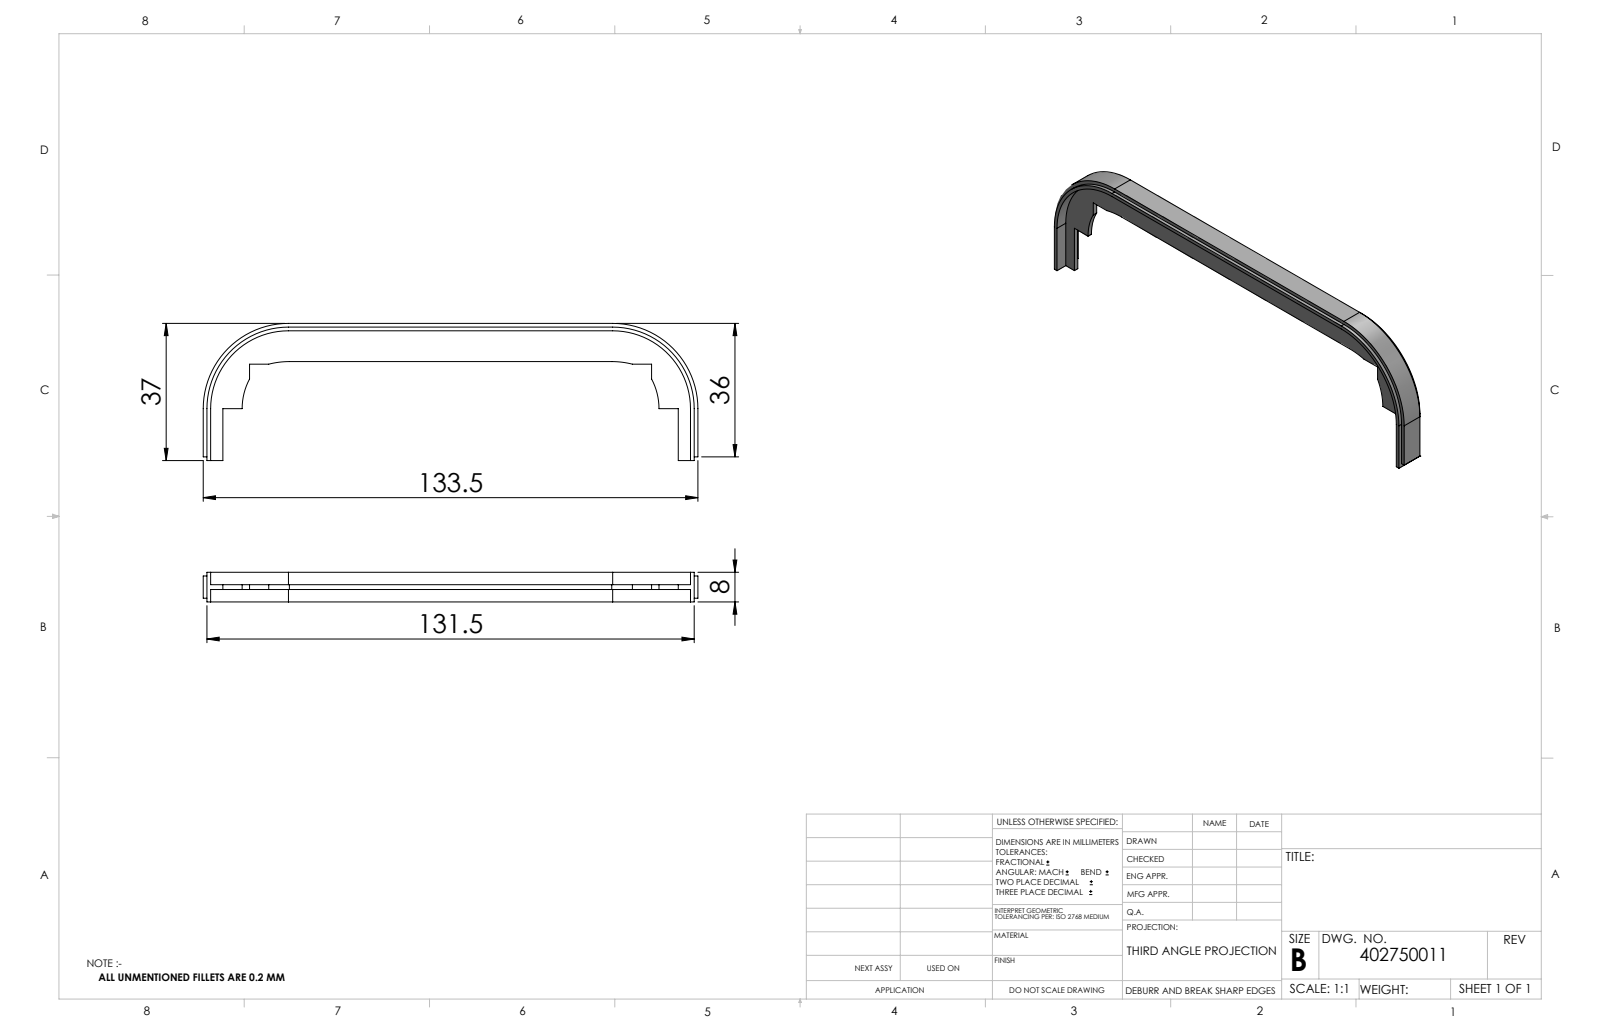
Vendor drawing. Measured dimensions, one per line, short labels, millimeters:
name: 402750011_c_1
written by: SolidWorks 2014 (CONFIG_CONTROL_DESIGN)
unit: mm
bodies: 1 solid, 46 faces (32 planar, 14 cylindrical, 0 other)
size: 133.5 × 37 × 8
volume: 4 172 mm³; area: 6 172 mm²
rounds: 2× R17, 2× R21, 2× R22, 2× R22.5, 2× R23
face distances: 1.3, 1, 2, 2.35, 3.65, 3.35, 4.65, 7, 131.5, 6
